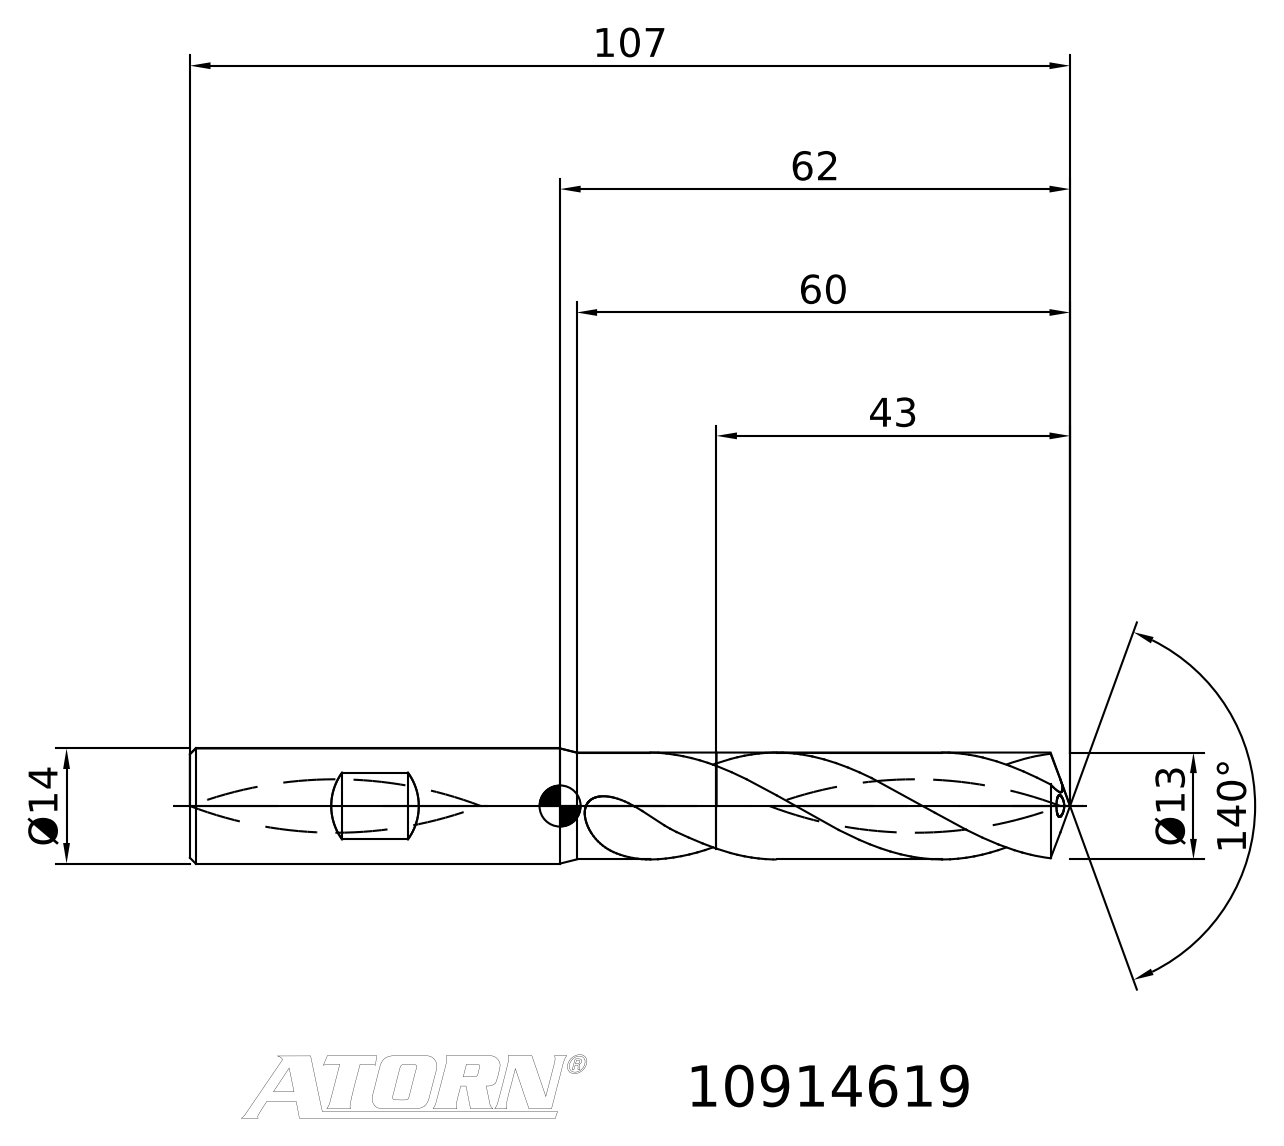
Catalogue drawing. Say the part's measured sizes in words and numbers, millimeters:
Its 3-D file was written by "TDM (AUTOMOTIVE_DESIGN)". It is 2 solids with 32 faces: 8 planar, 0 cylindrical and 24 other. Overall it measures 107 by 15.93 by 14 millimeters. Its volume is 12 463 cubic millimeters and its surface area 5 053 square millimeters. The main face-to-face distances are 64, 41.23, 105.23.
